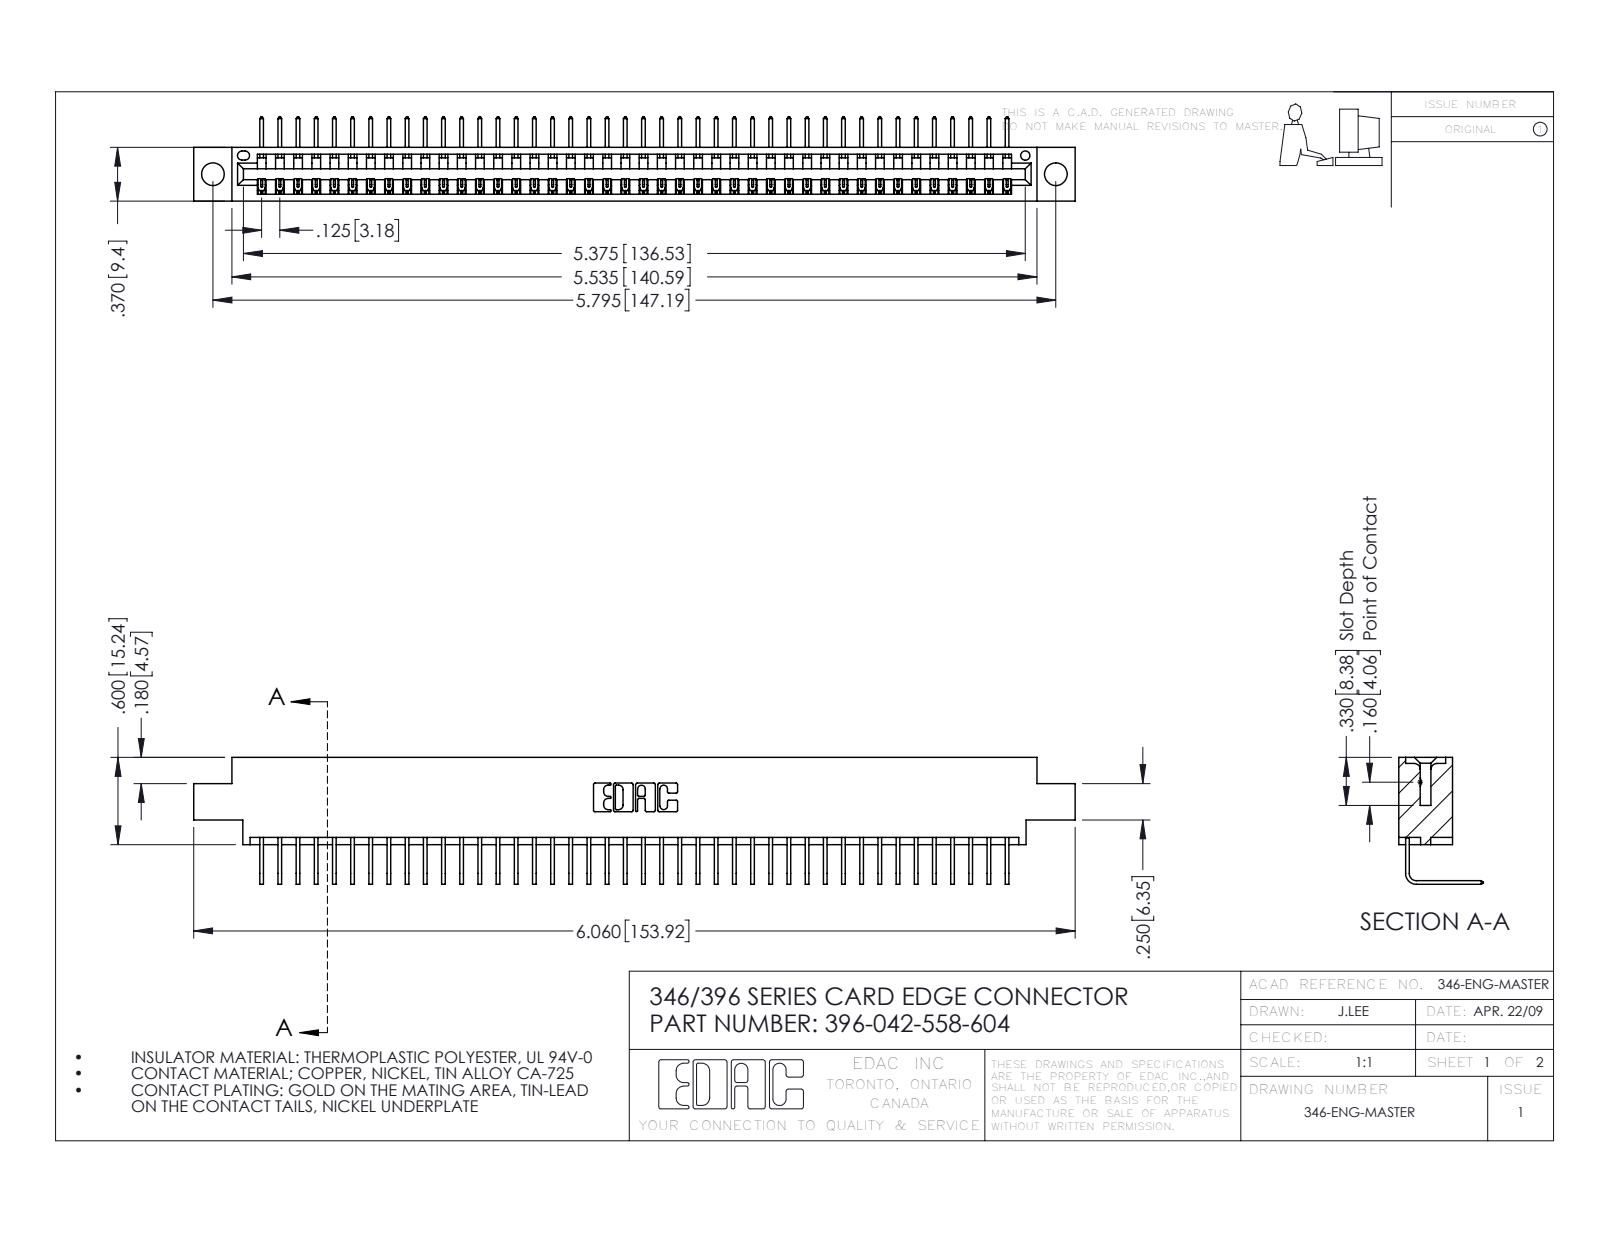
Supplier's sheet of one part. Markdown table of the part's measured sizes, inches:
| quantity | value |
| --- | --- |
| part name | 346 Part_0.170 Offset - 0.156 Dia-TH; 396-042-558-604; 345-292-001_558 Tail - 2 |
| STEP written by | SolidWorks 2016 (CONFIG_CONTROL_DESIGN) |
| units | inches |
| bodies | 43 solids, 2646 faces (1844 planar, 802 cylindrical, 0 other) |
| overall size | 6.06 × 0.873 × 0.58 |
| volume | 0.893 in³ |
| surface area | 29.59 in² |
| round holes (diameter × count) | 0.156 × 2, 0.064 × 1 |
| partial cylindrical surfaces (radius × count) | 0.006 × 84, 0.01 × 22, 0.007 × 6, 0.031 × 6, 0.026 × 3, 0.031 × 2, 0.04 × 2, 0.014 × 1 |
| main face-to-face distances | 0.322, 0.048, 0.37, 0.25, 0.298, 0.025, 0.072, 0.148, 0.222, 0.1 |
| hole center spacings | 0.246, 5.586, 5.795 |
